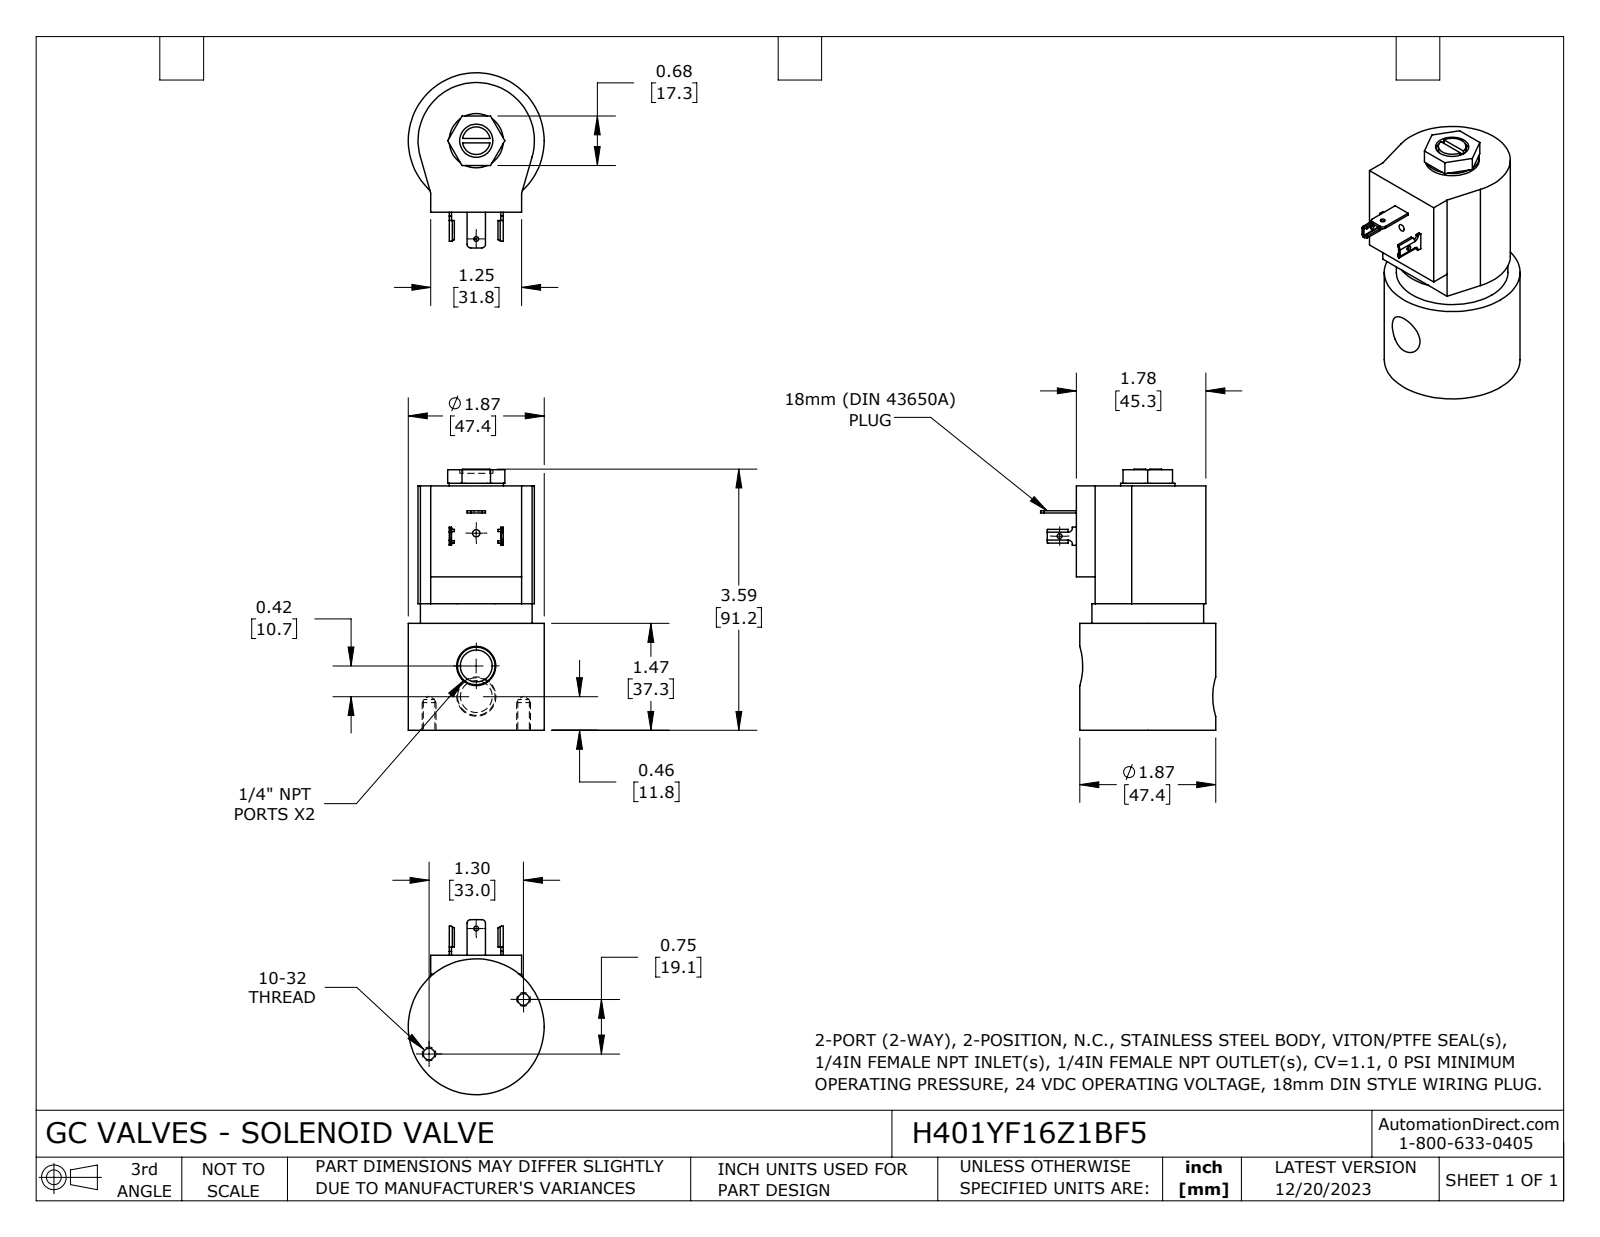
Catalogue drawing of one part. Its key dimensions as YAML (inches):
part_name: "H401YF16Z1BF5"
step_written_by: "SolidWorks 2023 (CONFIG_CONTROL_DESIGN)"
units: inches
bodies: {solids: 1, faces: 132, planar: 75, cylindrical: 43, other: 14}
overall_size: [3.591, 2.407, 1.868]
volume: 8.118
surface_area: 29.18
round_holes:
  - {diameter: 0.159, count: 2}
  - {diameter: 0.438, count: 2}
  - {diameter: 0.066, count: 1}
  - {diameter: 0.067, count: 1}
  - {diameter: 0.1, count: 1}
  - {diameter: 0.456, count: 1}
round_bosses_or_shafts:
  - {diameter: 1.868, count: 1}
  - {diameter: 1.535, count: 1}
  - {diameter: 0.746, count: 1}
  - {diameter: 0.38, count: 1}
partial_cylinders:
  - {radius: 0.006, count: 4}
  - {radius: 0.041, count: 4}
  - {radius: 0.05, count: 2}
  - {radius: 0.06, count: 2}
  - {radius: 0.8, count: 1}
face_to_face_distances: [3.36, 1.47, 1.89, 0.26, 2.11, 0.64, 1.25, 1.25, 3.583, 2.113]
hole_center_spacings: [0.75, 0.422, 1.171, 1.35, 1.5, 1.824, 1.843, 2.246]
